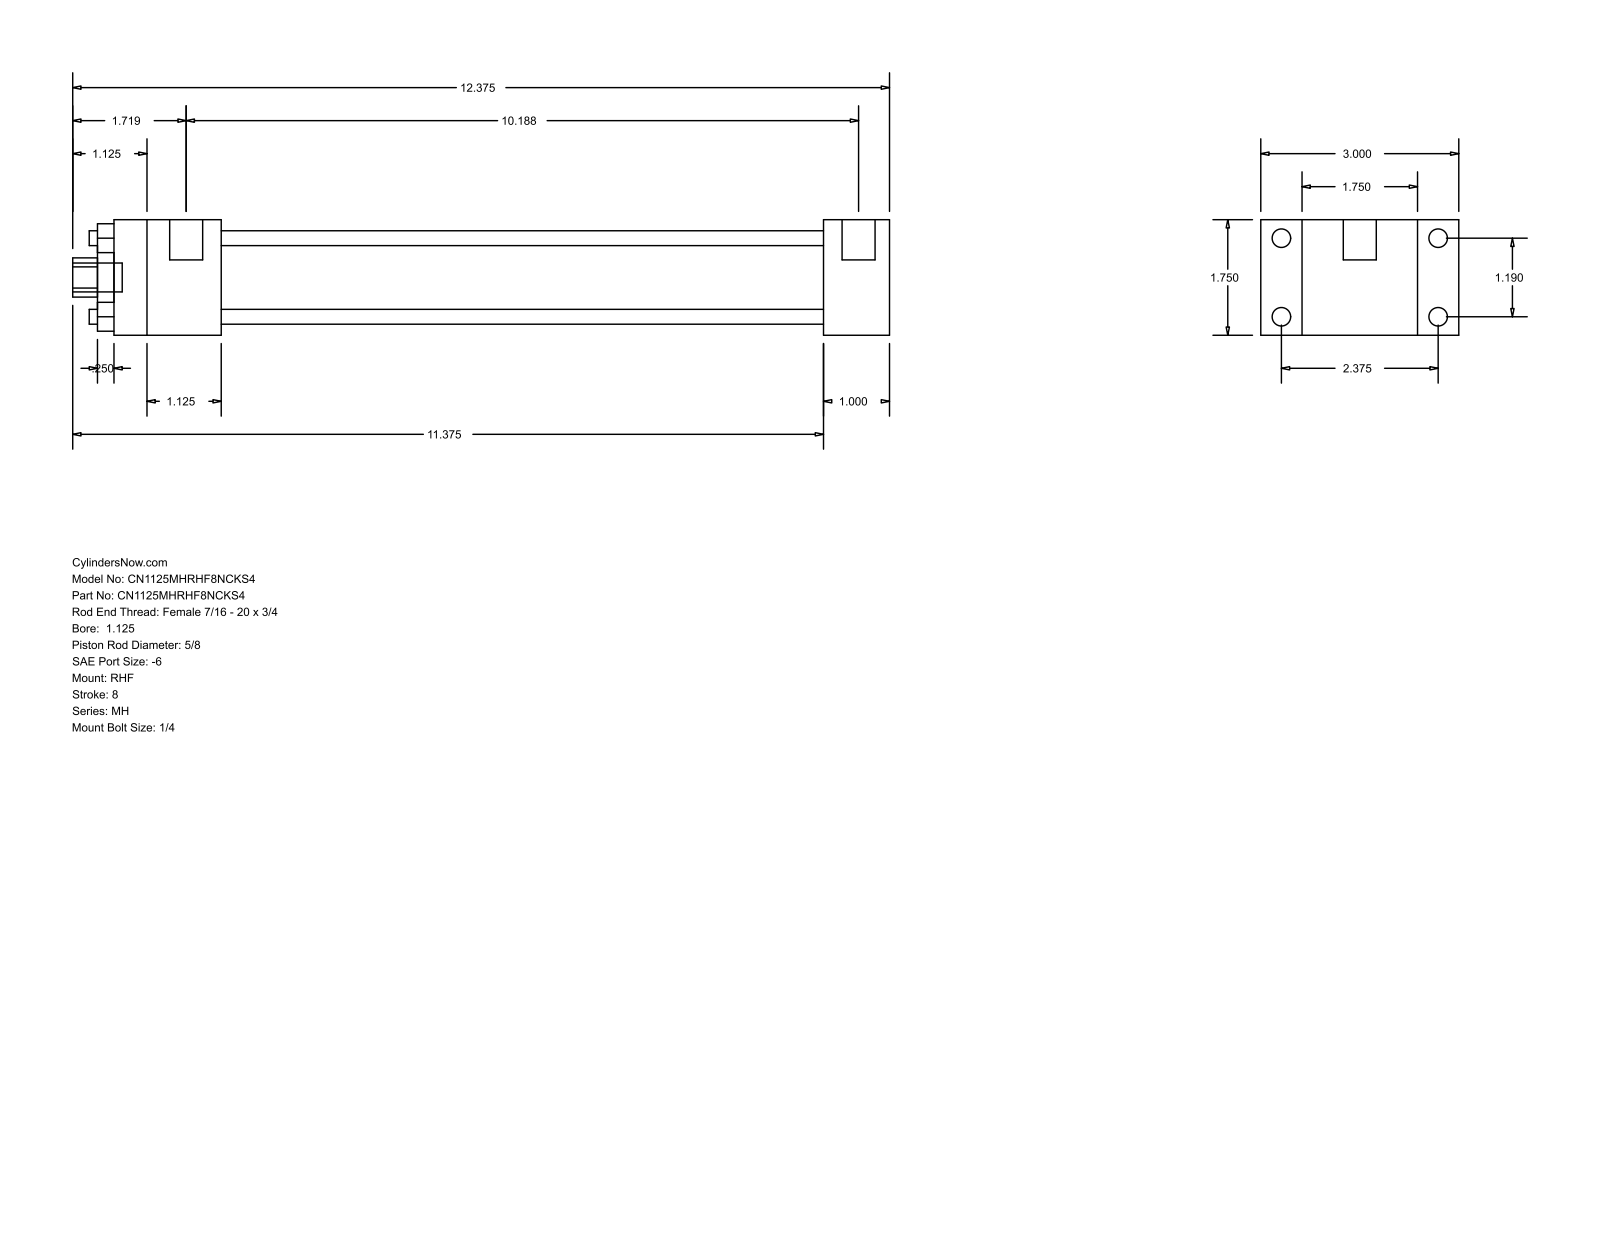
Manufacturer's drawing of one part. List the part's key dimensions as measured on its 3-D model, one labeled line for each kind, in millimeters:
Part name (STEP PRODUCT): MH_RHF__0112_0.625
STEP written by: GSSL Pune (CONFIG_CONTROL_DESIGN)
Units: millimetres
Bodies: 0 solids, 88 faces (60 planar, 28 cylindrical, 0 other)
Overall size (bounding box): 314.32 × 76.2 × 44.45
Round holes (diameter × count): ⌀5.71 ×4, ⌀15.88 ×1, ⌀28.57 ×1, ⌀34.92 ×1
Round bosses / shafts (diameter × count): ⌀7.14 ×4, ⌀5.56 ×4, ⌀12.7 ×2, ⌀11.11 ×1
Partial cylindrical surfaces — rounded edges, fillets, slot ends (radius × count): R7.54 ×1
Main face-to-face distances: 44.46, 15.87, 60.33, 25.39, 76.2, 231.78, 257.17, 41.27, 273.05, 298.44
Hole centre spacings: 21.37, 30.22, 42.74
